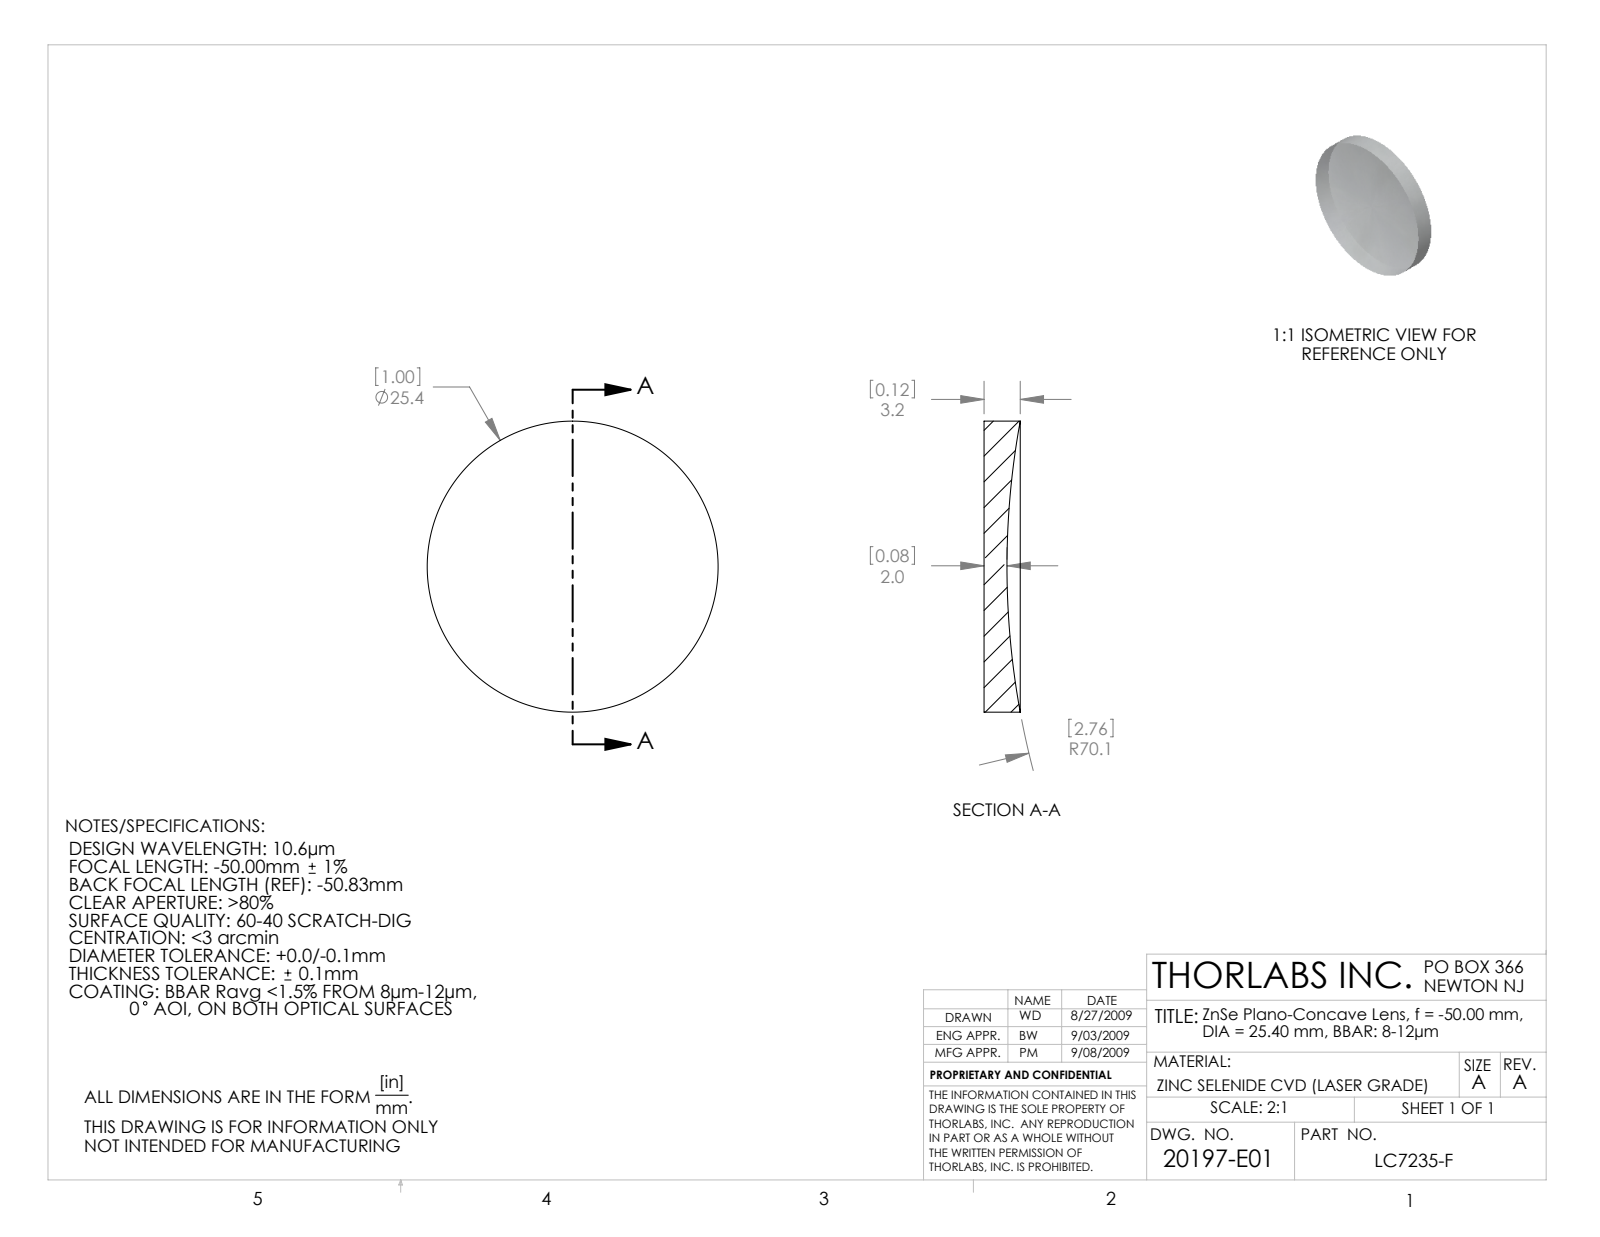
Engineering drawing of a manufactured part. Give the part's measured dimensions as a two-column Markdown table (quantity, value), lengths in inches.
| quantity | value |
| --- | --- |
| part name | 20197-E0W |
| STEP written by | SolidWorks 2007 (CONFIG_CONTROL_DESIGN) |
| units | inches |
| bodies | 1 solid, 5 faces (1 planar, 2 cylindrical, 2 other) |
| overall size | 1 × 1 × 0.124 |
| volume | 0.08 in³ |
| surface area | 1.969 in² |
| round bosses / shafts (diameter × count) | 1 × 1 |
